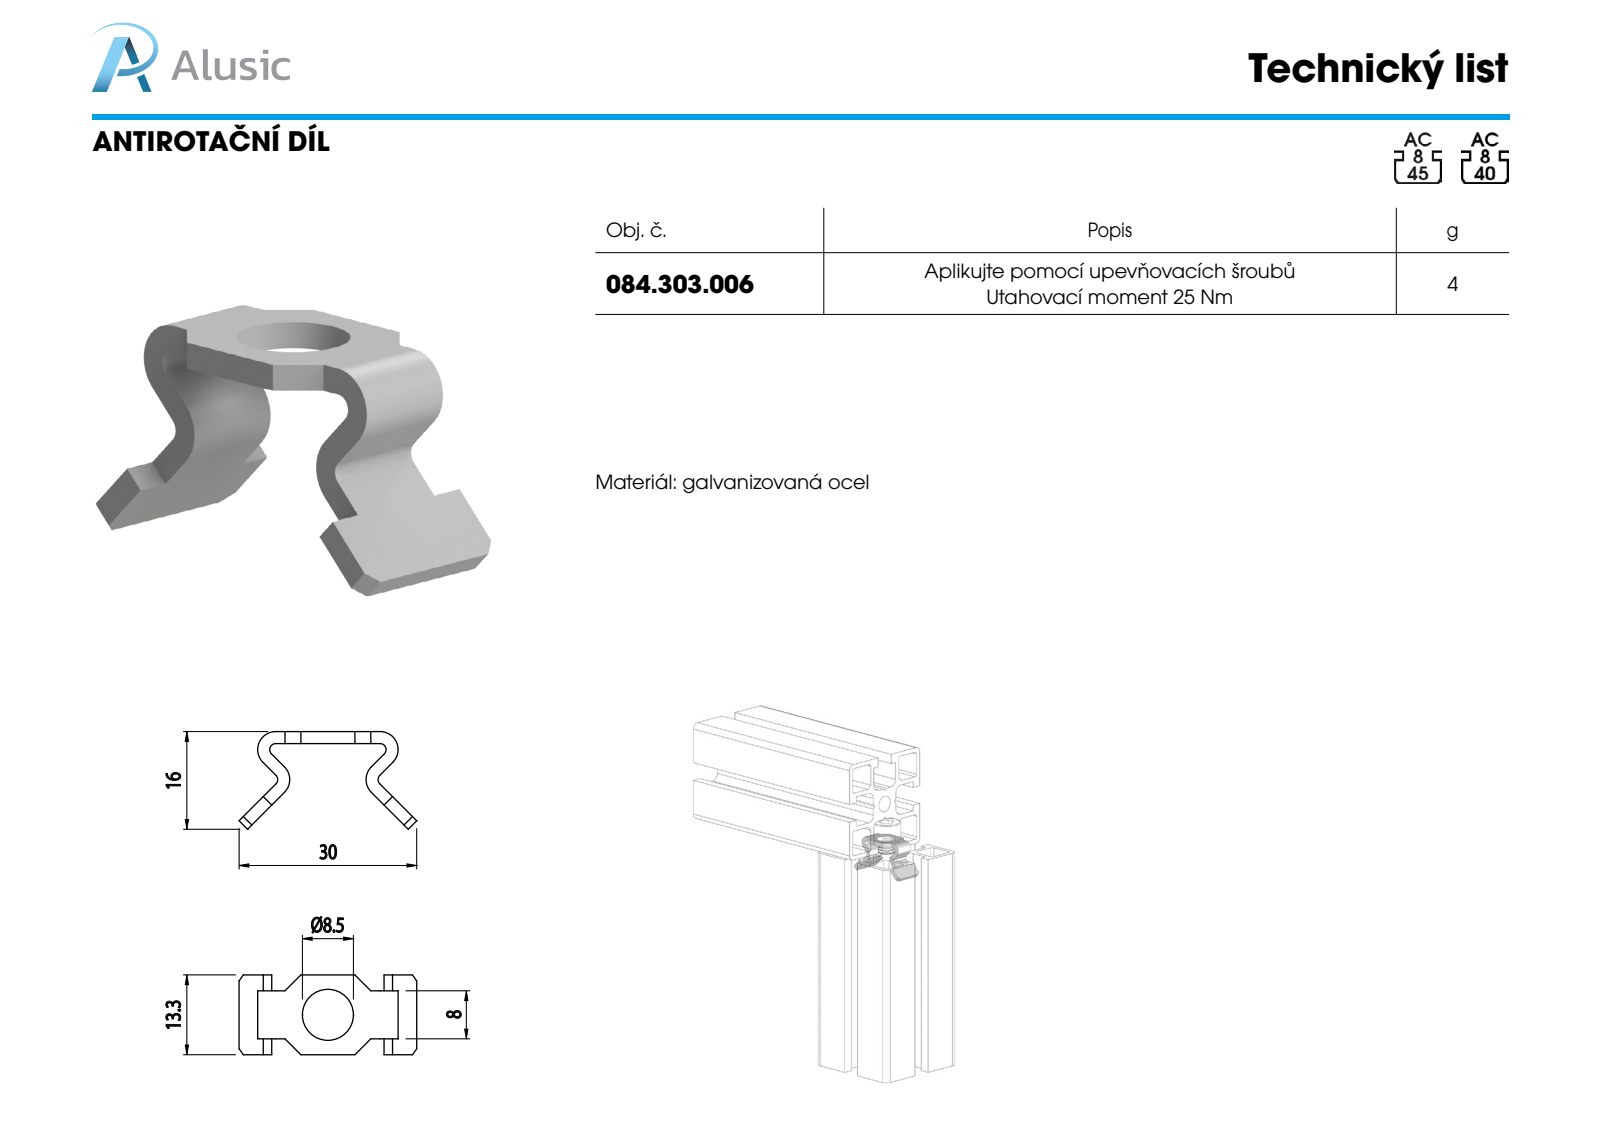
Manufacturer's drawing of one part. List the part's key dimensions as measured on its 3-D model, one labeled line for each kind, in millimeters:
Part name (STEP PRODUCT): 084.303.006; 210814
STEP written by: SolidWorks 2011 (CONFIG_CONTROL_DESIGN)
Units: millimetres
Bodies: 1 solid, 64 faces (50 planar, 14 cylindrical, 0 other)
Overall size (bounding box): 29.61 × 16.27 × 13.3
Volume: 1 033 mm³ · Surface area: 1 392 mm²
Round holes (diameter × count): ⌀8.5 ×1
Partial cylindrical surfaces — rounded edges, fillets, slot ends (radius × count): R1 ×4, R3 ×4
Main face-to-face distances: 2, 9.23, 2.65, 10.65, 8, 7.23, 11.23, 9.7, 11.7, 18.93
